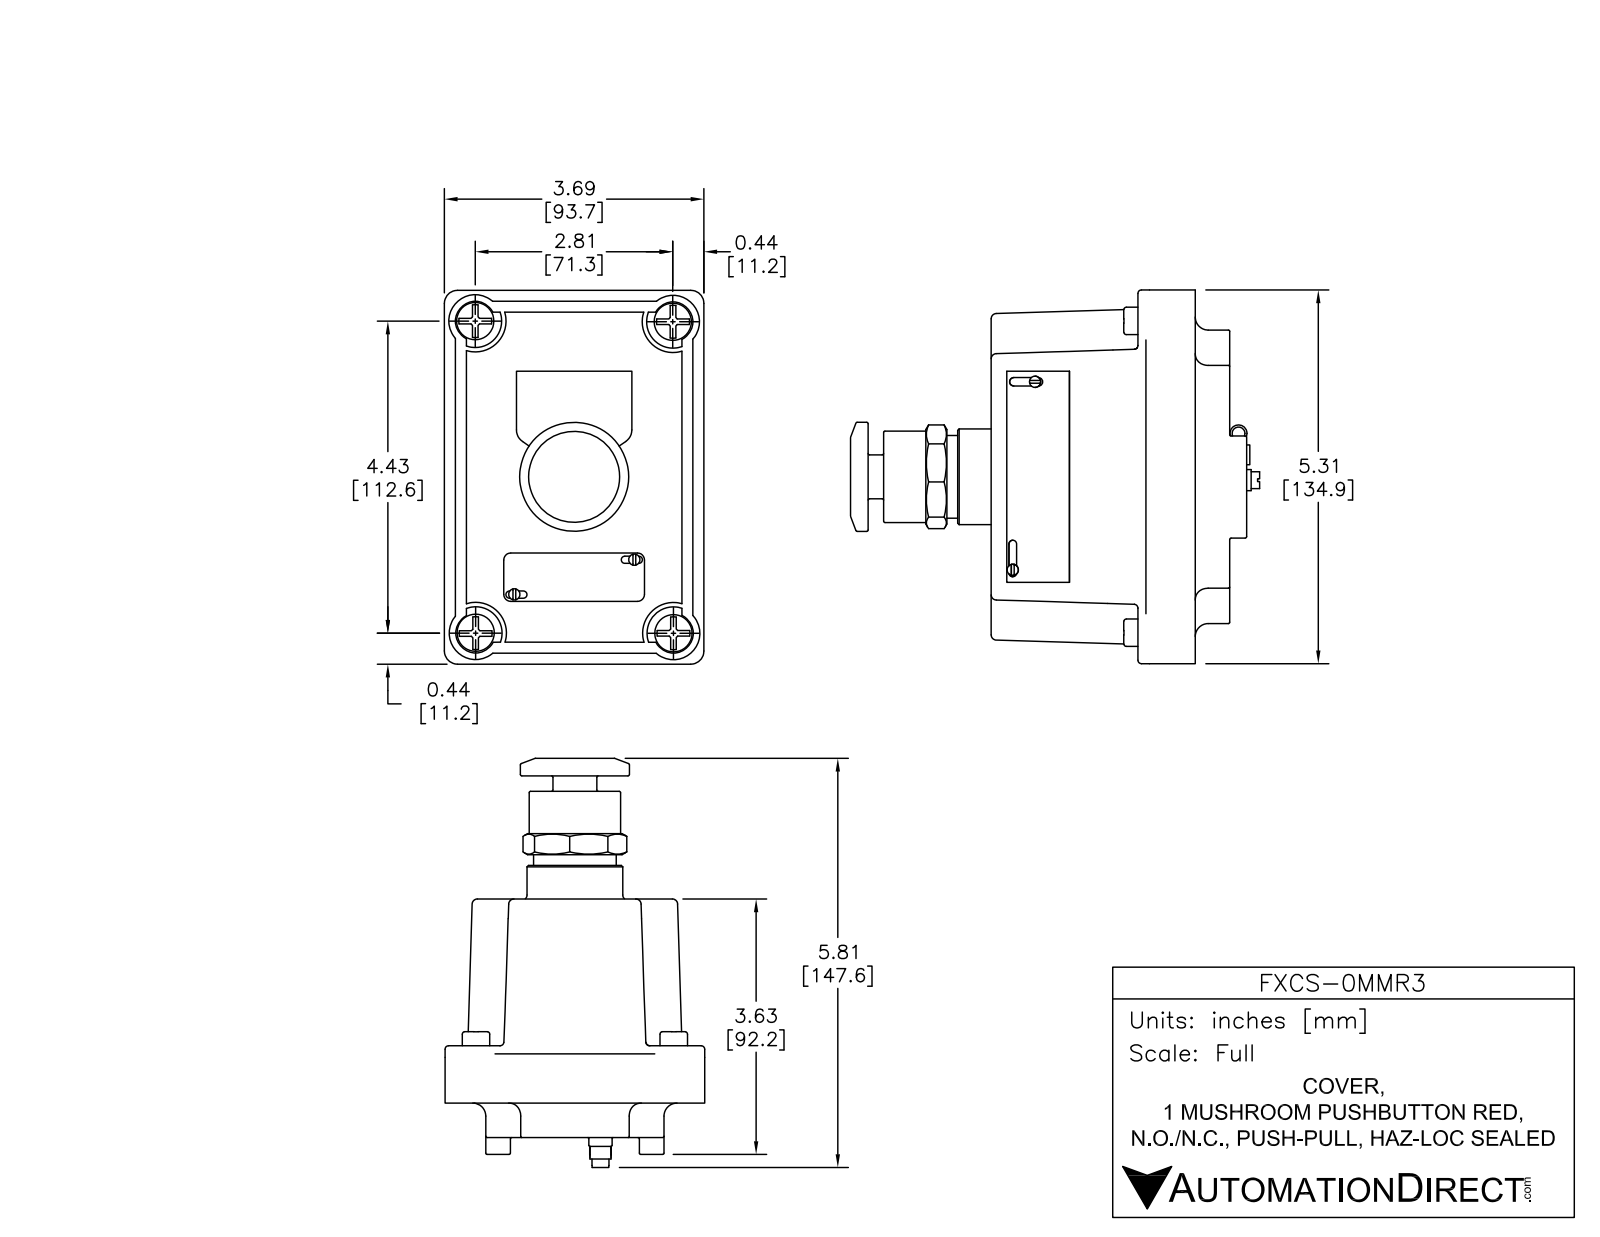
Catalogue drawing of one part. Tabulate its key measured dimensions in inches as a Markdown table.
| quantity | value |
| --- | --- |
| part name | FXCS-0MMR3 |
| STEP written by | SolidWorks 2015 (AUTOMOTIVE_DESIGN) |
| units | inches |
| bodies | 1 solid, 732 faces (302 planar, 155 cylindrical, 275 other) |
| overall size | 5.888 × 5.31 × 3.69 |
| volume | 50.6 in³ |
| surface area | 104.6 in² |
| round holes (diameter × count) | 0.16 × 8, 0.198 × 1 |
| round bosses / shafts (diameter × count) | 0.16 × 6, 0.39 × 4, 1.55 × 1, 1.36 × 1, 1.3 × 1, 1.175 × 1, 0.623 × 1, 0.33 × 1 |
| partial cylindrical surfaces (radius × count) | 0.02 × 22, 0.05 × 12, 0.051 × 4, 0.055 × 4, 0.06 × 4, 0.075 × 4, 0.1 × 4, 0.185 × 4 |
| main face-to-face distances | 0.49, 3.39, 2.9, 0.02, 3.69, 0.578, 3.111, 1.19, 0.7, 2.2 |
| hole center spacings | 0.25, 2.197, 0.5, 2.183, 2.239, 0.75, 2.308, 0.728 |
